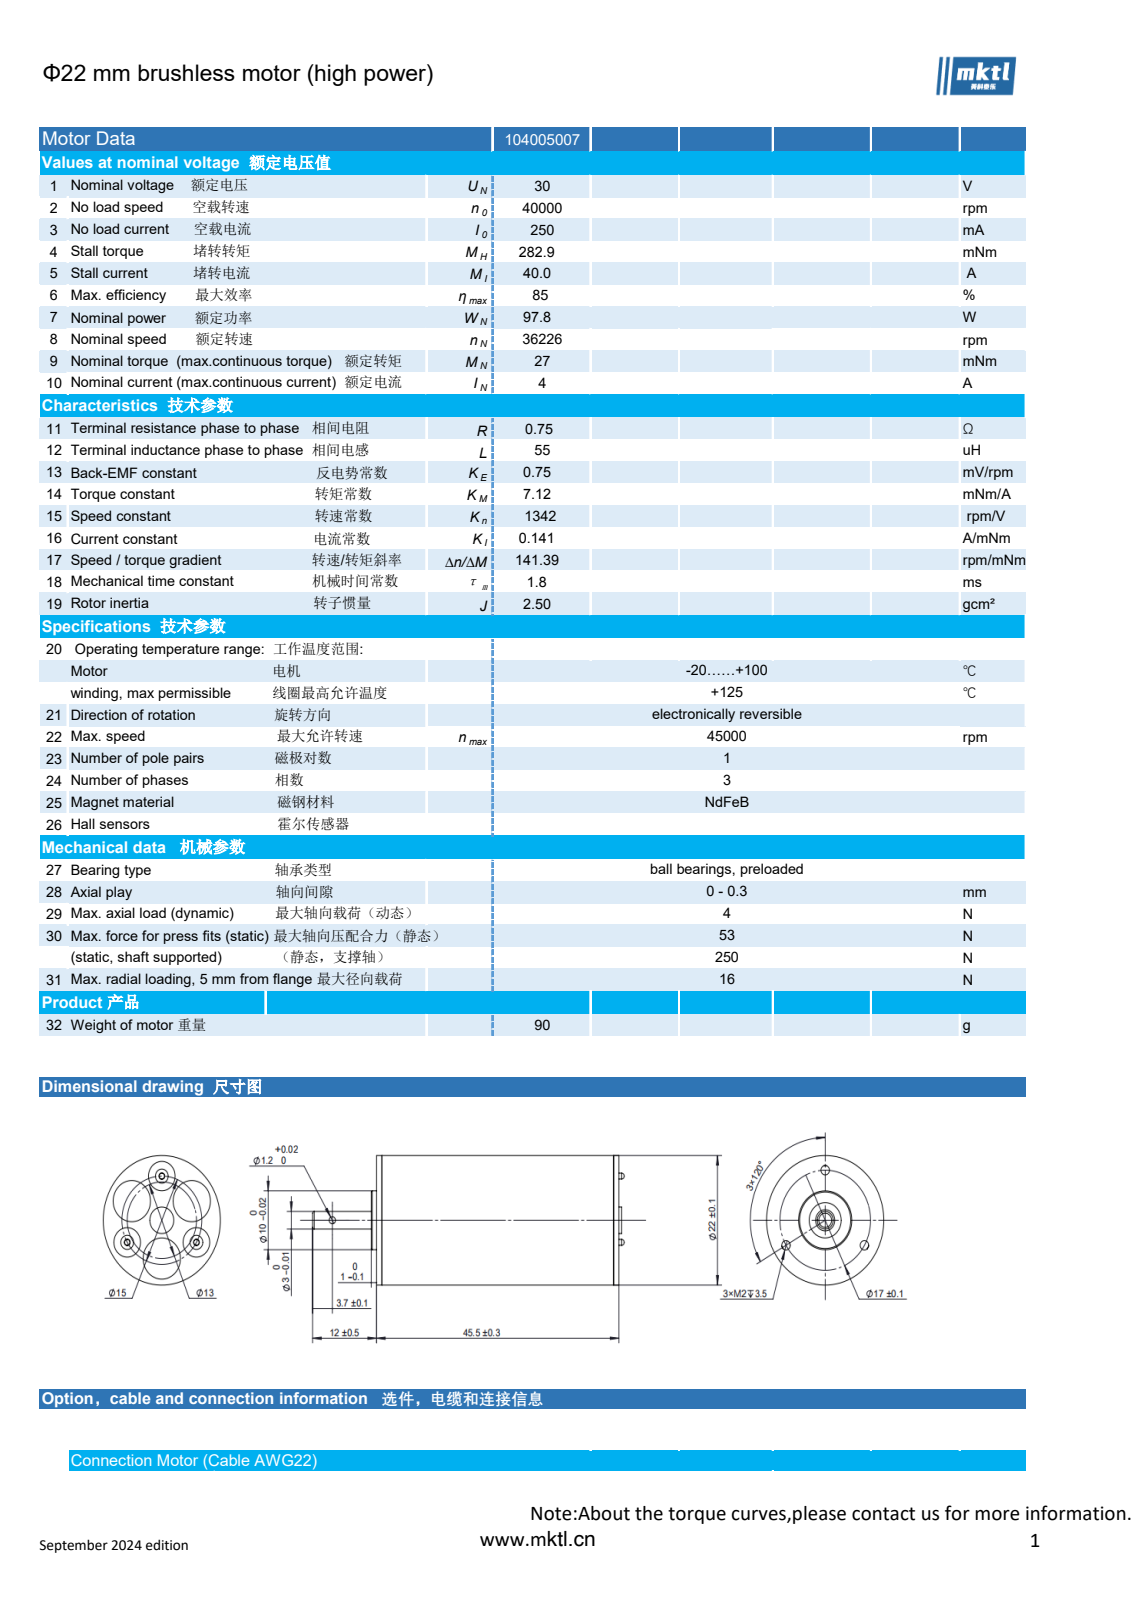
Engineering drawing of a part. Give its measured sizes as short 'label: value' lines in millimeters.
name: approval 104005007
written by: SolidWorks 2018 (CONFIG_CONTROL_DESIGN)
unit: mm
bodies: 171 solids, 1226 faces (391 planar, 793 cylindrical, 42 other)
size: 58.5 × 22 × 22
volume: 13 658 mm³; area: 58 104 mm²
holes: 4× ⌀1.2, 3× ⌀1.1, 3× ⌀1.6, 3× ⌀2.1, 3× ⌀2.5, 3× ⌀5, 3× ⌀7, 1× ⌀3, 1× ⌀3.1, 1× ⌀6, 1× ⌀8, 1× ⌀11.2
bosses: 3× ⌀2.4, 3× ⌀1.5, 3× ⌀1, 3× ⌀0.3, 1× ⌀22, 1× ⌀21.1, 1× ⌀20.9, 1× ⌀20.8
rounds: 9× R0.5, 3× R1.5, 3× R1.7, 1× R5.75, 1× R6.25, 1× R8.75
face distances: 0.4, 0.6, 0.8, 1, 1.2, 1.4, 1.6, 1.8, 2, 2.2
hole spacings: 7.7, 7.05, 13.87, 6.5, 7.5, 8.5, 11.26, 14
